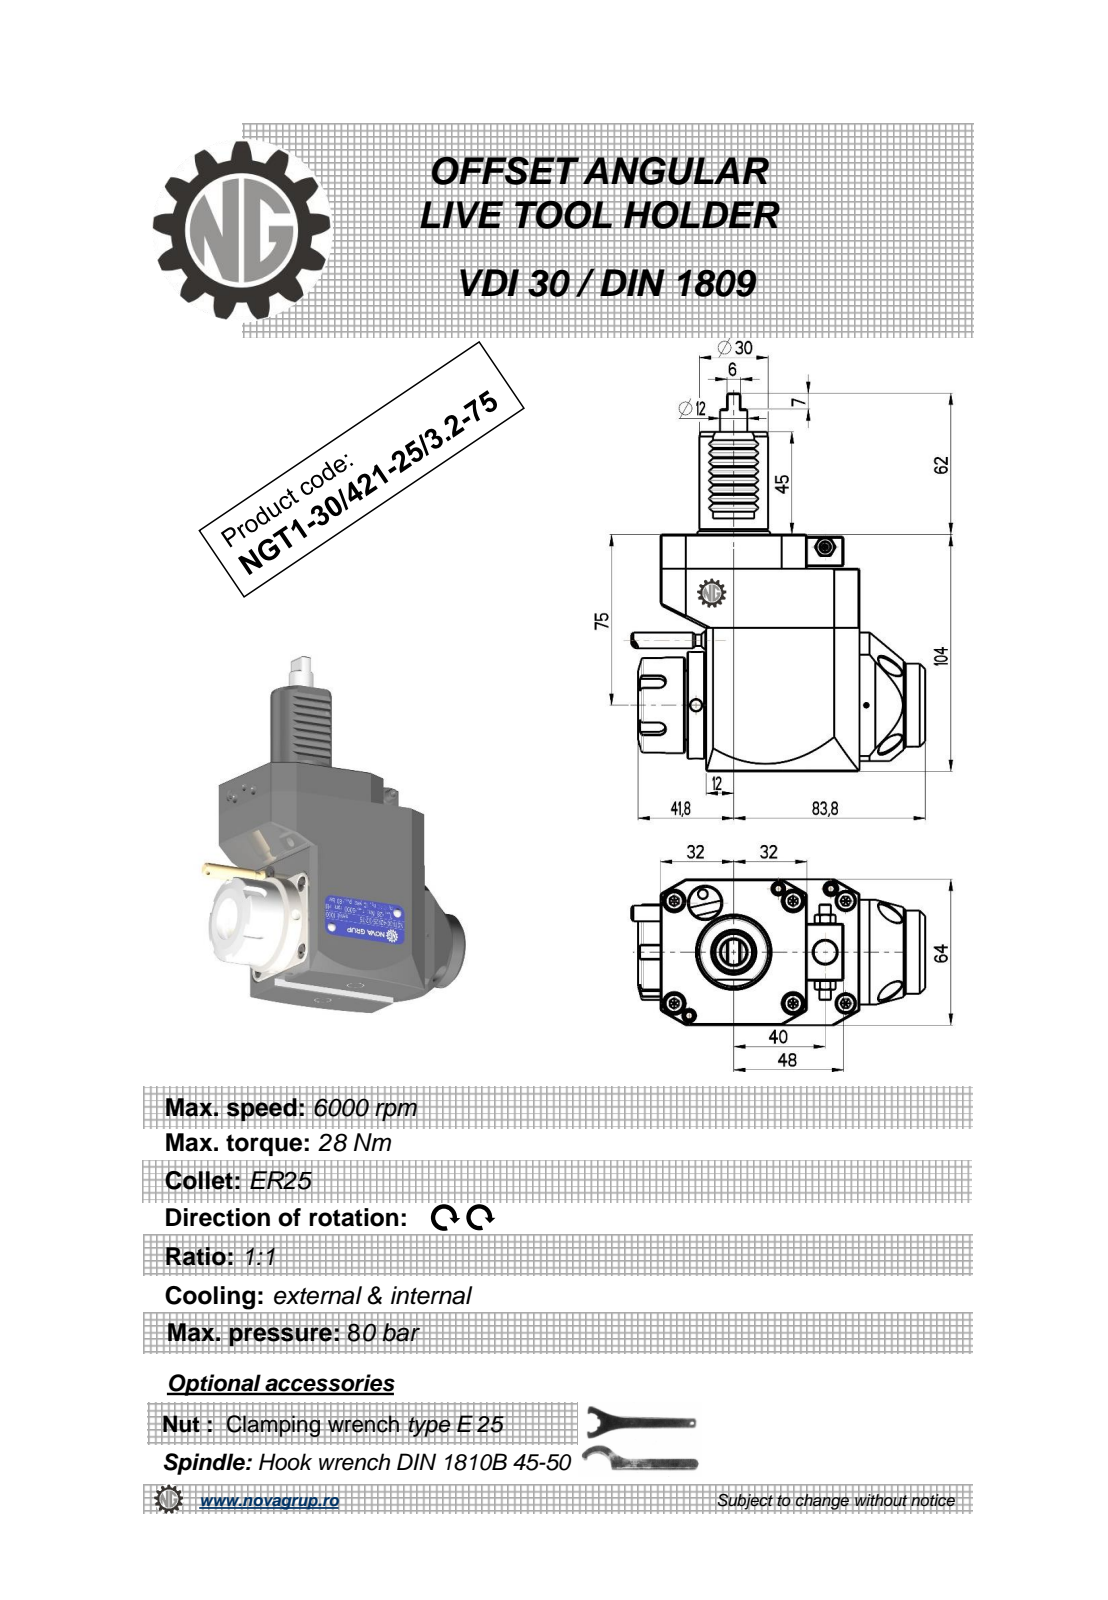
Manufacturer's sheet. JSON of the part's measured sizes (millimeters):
{"part_name": "NGT1_30_421_25_3_2_75", "step_written_by": "PRO/ENGINEER BY PARAMETRIC TECHNOLOGY CORPORATION, 2010280 (CONFIG_CONTROL_DESIGN)", "units": "millimeters", "bodies": {"solids": 1, "faces": 421, "planar": 193, "cylindrical": 82, "other": 146}, "overall_size": [166, 128.63, 64], "volume_mm3": 580980, "surface_area_mm2": 55331, "round_holes": [[5, 2], [2.5, 1], [3, 1], [4.2, 1], [9.5, 1], [10, 1], [20.3, 1]], "round_bosses_or_shafts": [[5, 2], [47, 1], [42, 1], [36.5, 1], [35, 1], [30, 1], [12, 1], [8.96, 1]], "partial_cylinders_radius": [[0.26, 12], [0.3, 8], [3, 5], [0.8, 2], [160, 2], [32, 1]], "face_to_face_distances": [64, 104, 15, 87, 89, 20, 19.8, 0.5, 67.2, 67], "hole_center_spacings": [33.19, 43, 56.45, 68, 89.54]}
